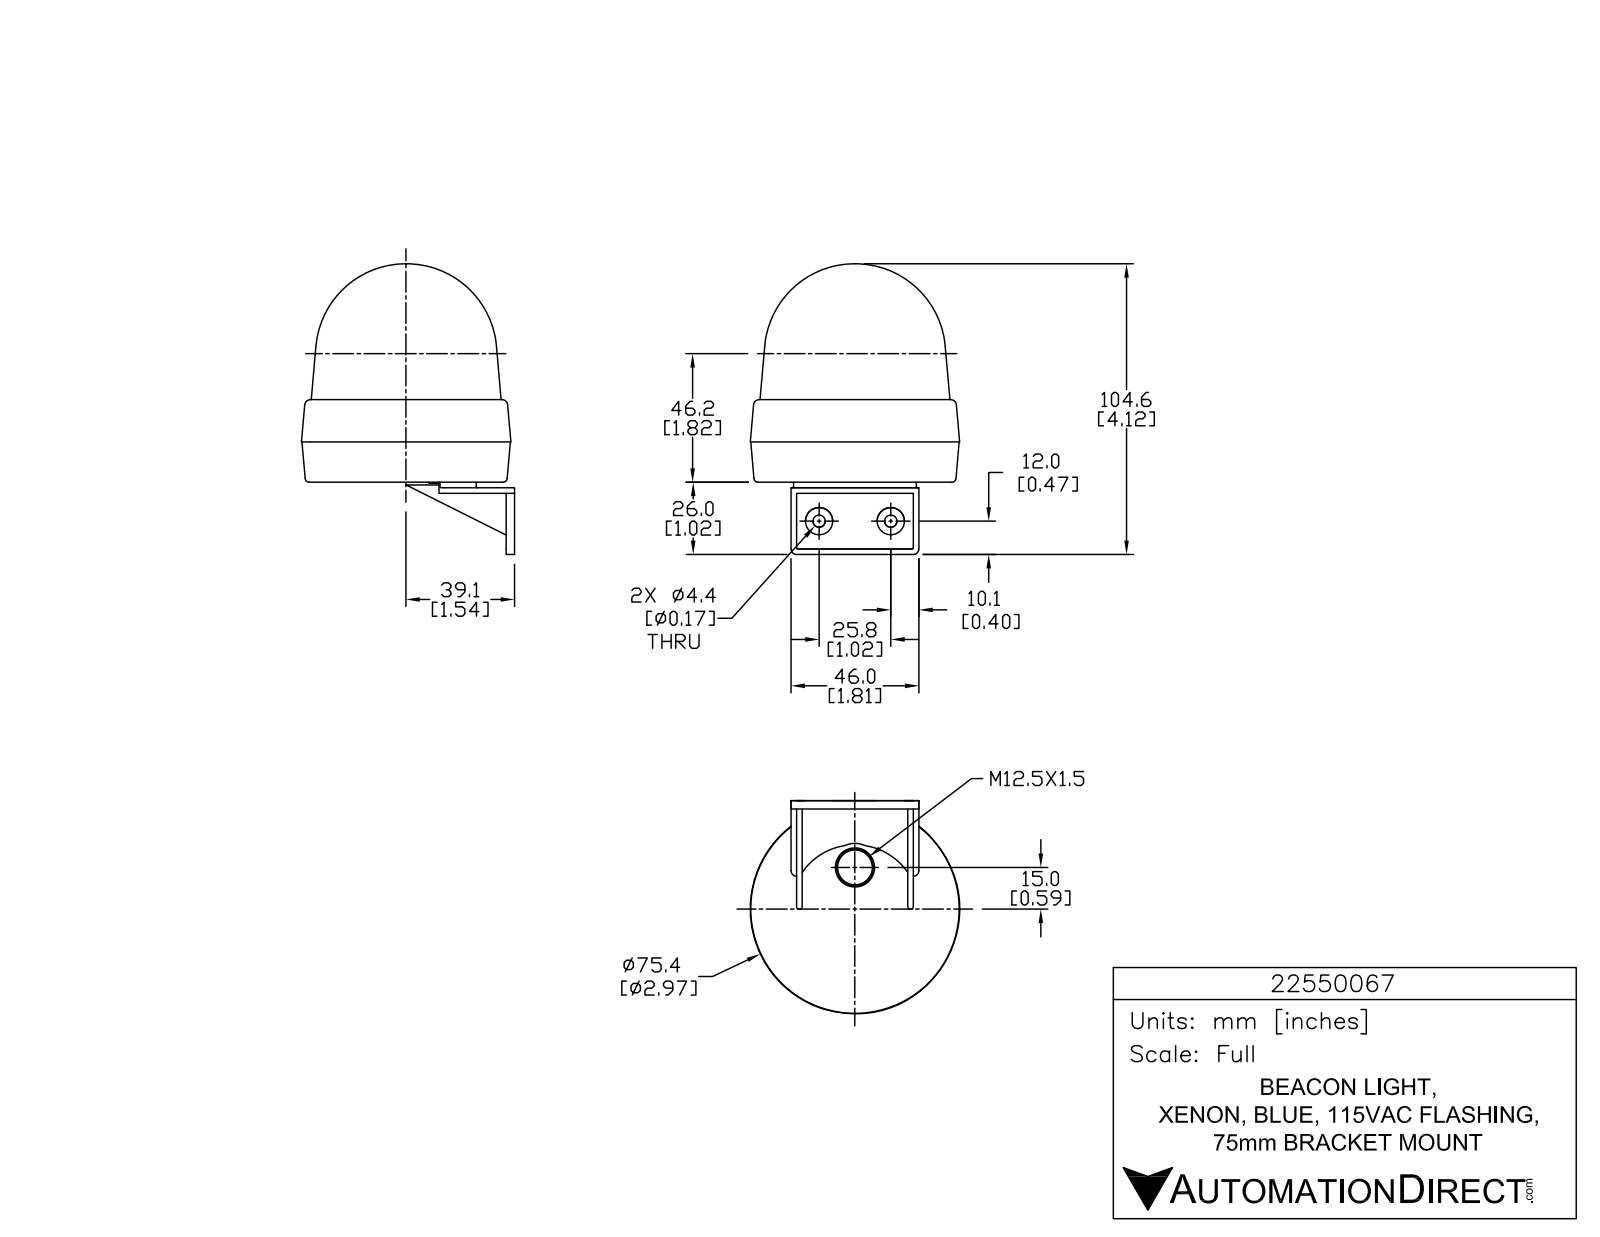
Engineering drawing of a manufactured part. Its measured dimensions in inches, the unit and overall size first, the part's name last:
Units: inches
Overall size (bounding box): 4.117 × 3.253 × 2.967
Round holes (diameter × count): ⌀0.059 ×3, ⌀0.173 ×2
Round bosses / shafts (diameter × count): ⌀0.339 ×3, ⌀0.084 ×3, ⌀0.386 ×2
Partial cylindrical surfaces — rounded edges, fillets, slot ends (radius × count): R0.005 ×9, R0.005 ×6, R0.012 ×6, R0.012 ×6, R0.012 ×6, R0.02 ×6, R0.196 ×6, R0.079 ×4
Main face-to-face distances: 0.079, 0.157, 1.574, 0.039, 0.118, 1.653, 1.496, 0.079, 1.654, 1.732
Hole centre spacings: 1.016
Volume: 16.02 in³ · Surface area: 41.97 in²
Bodies: 1 solid, 819 faces (549 planar, 180 cylindrical, 90 other)
Part name (STEP PRODUCT): 22550067
STEP written by: SolidWorks 2015 (AUTOMOTIVE_DESIGN)
